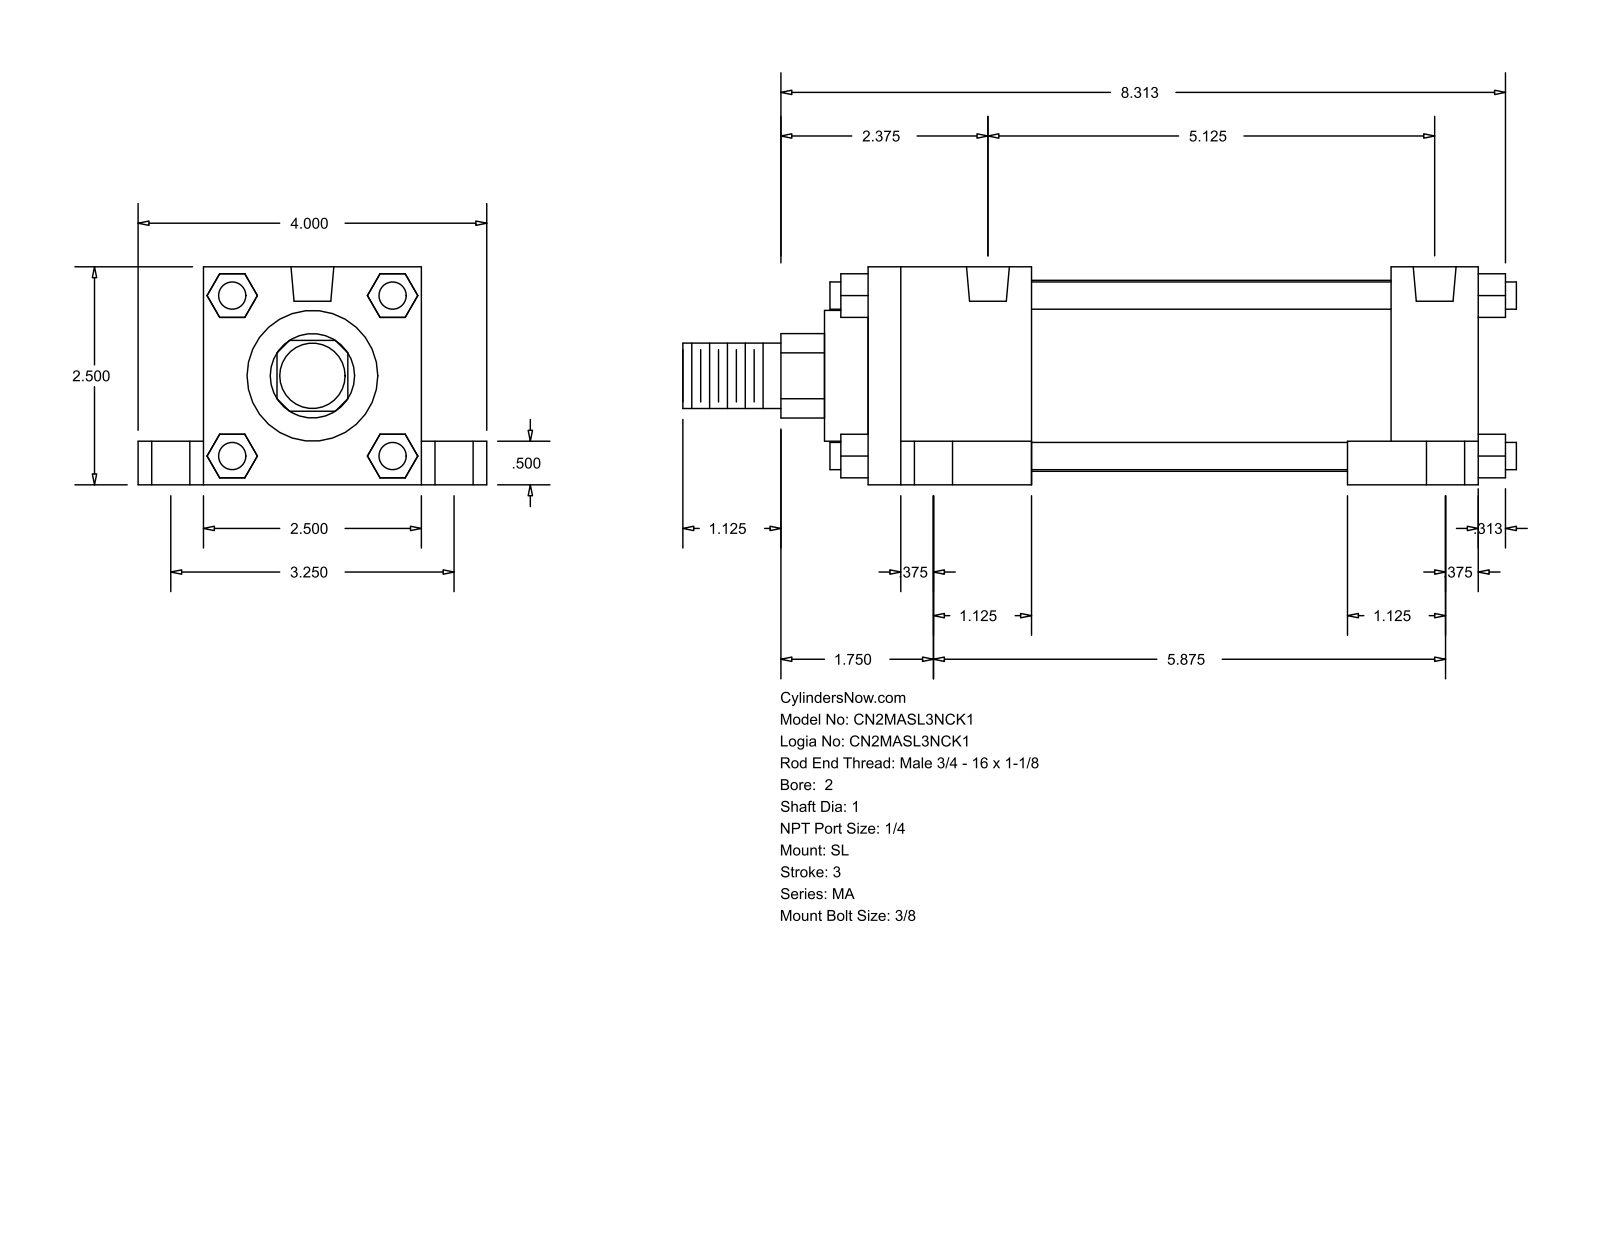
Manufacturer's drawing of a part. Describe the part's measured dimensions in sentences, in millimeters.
The part is named "MA_SL__0200_1". Its 3-D file was written by "GSSL Pune (CONFIG_CONTROL_DESIGN)". It is 0 solids with 148 faces: 112 planar, 36 cylindrical and 0 other. Overall it measures 242.89 by 101.6 by 63.5 millimeters. Round holes: 4 of diameter 7.94, 4 of diameter 11.11, 4 of diameter 17.46, 2 of diameter 12.49. Round bosses or shafts: 4 of diameter 7.94, 1 of diameter 55.63, 1 of diameter 38.1, 1 of diameter 25.4, 1 of diameter 19.05. Partial cylindrical surfaces (rounded edges, fillets, slot ends): 1 of radius 12.29. The main face-to-face distances are 63.5, 12.7, 177.8, 19.05, 82.55, 25.4, 50.8, 47.63, 130.17, 152.4. The hole center spacings are 41.39, 44.22, 82.54, 130.17, 139.59, 149.23, 151.77, 170.54.
